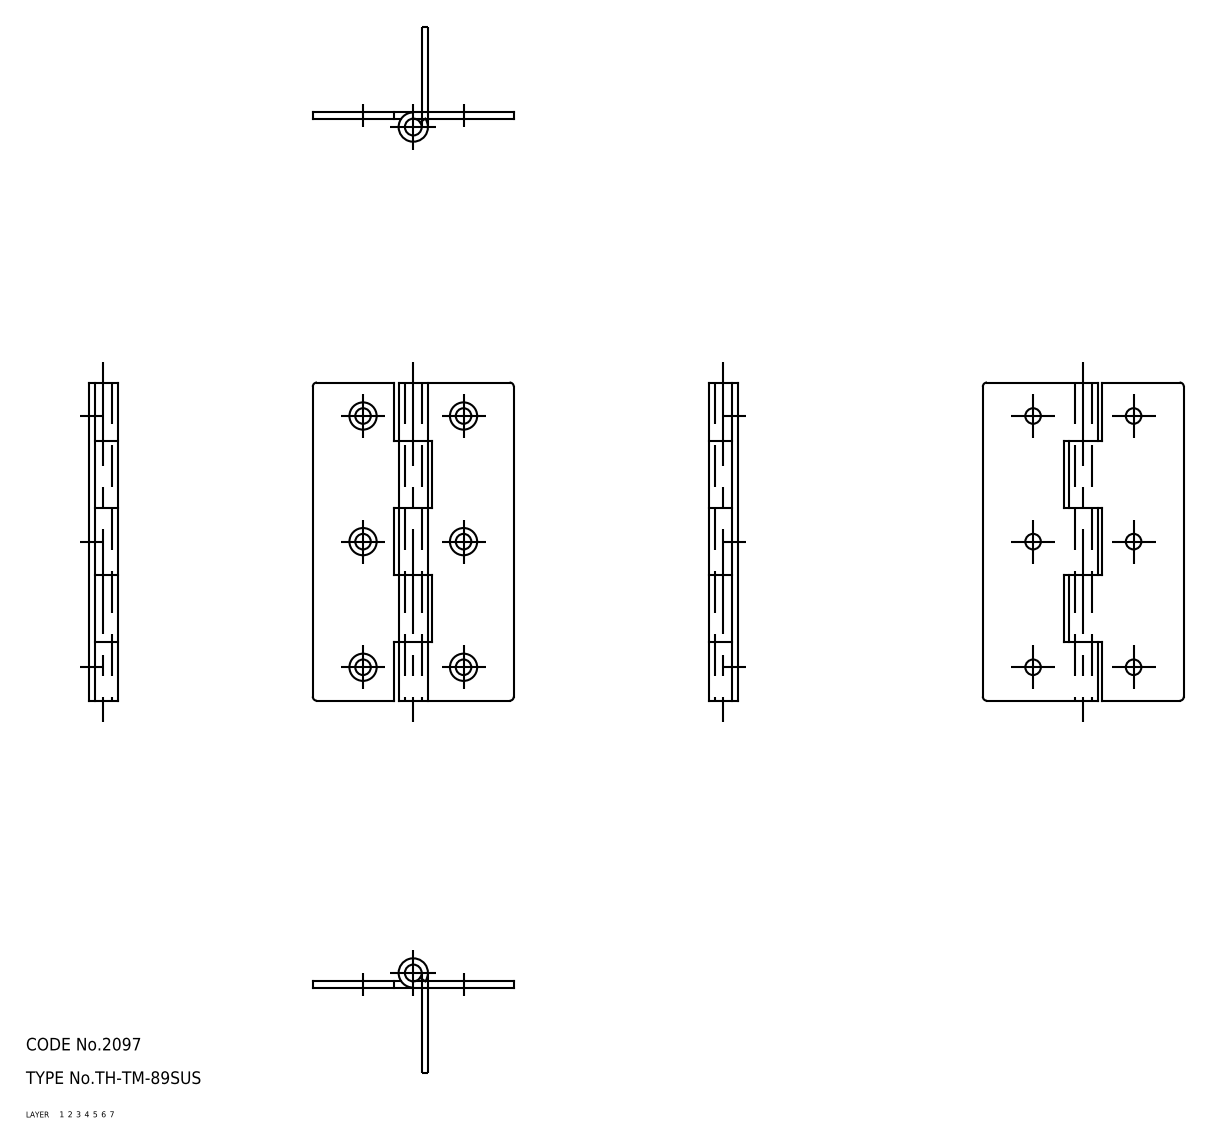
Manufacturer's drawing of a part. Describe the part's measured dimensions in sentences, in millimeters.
The part is named "shaft; hinge piece_B; hinge piece_A; TH_TM_89SUS_26637_36". Its 3-D file was written by "CADfix (AUTOMOTIVE_DESIGN)". It is 3 solids with 70 faces: 0 planar, 0 cylindrical and 70 other. Overall it measures 76 by 48 by 7 millimeters. Its volume is 7 395 cubic millimeters and its surface area 10 599 square millimeters.
